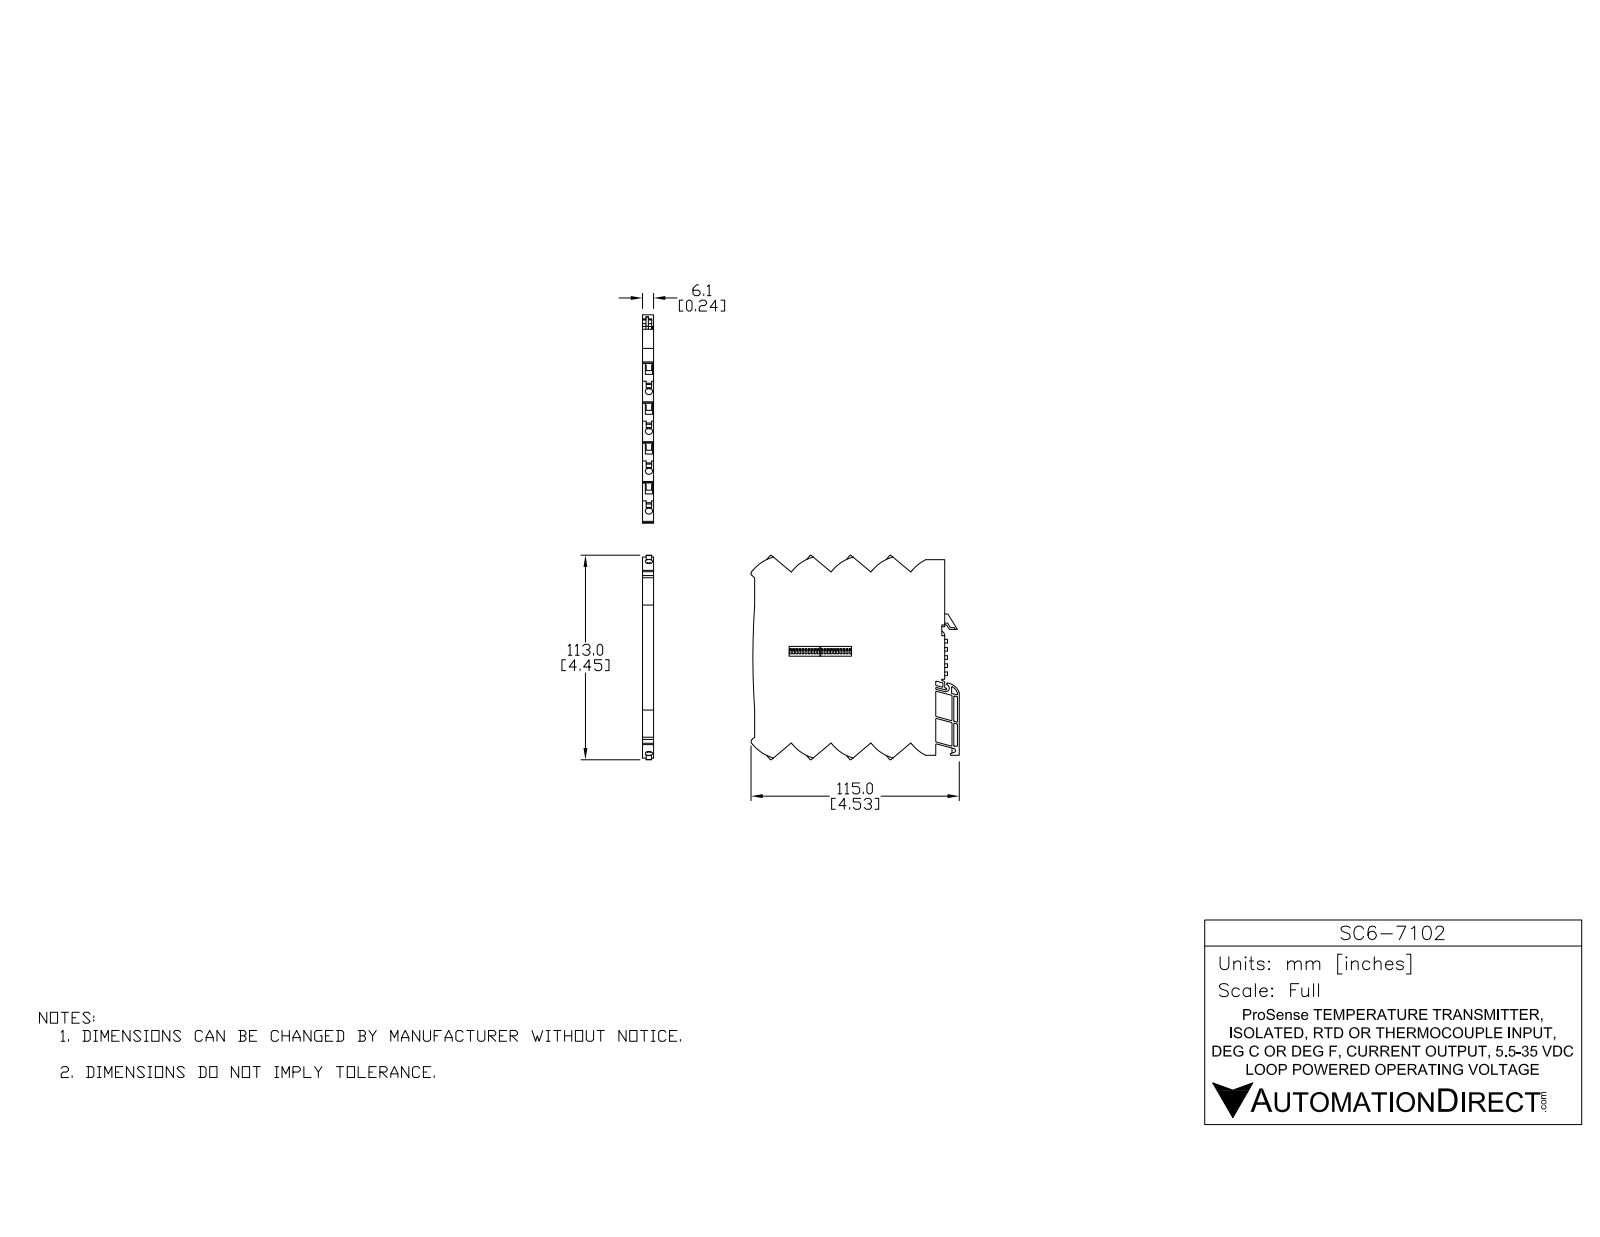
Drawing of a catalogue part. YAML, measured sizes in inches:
part_name: "SC6-7102"
step_written_by: "SolidWorks 2017 (AUTOMOTIVE_DESIGN)"
units: inches
bodies: {solids: 1, faces: 804, planar: 537, cylindrical: 107, other: 160}
overall_size: [4.528, 4.448, 0.24]
volume: 3.965
surface_area: 43.77
round_holes:
  - {diameter: 0.157, count: 8}
partial_cylinders:
  - {radius: 0.012, count: 33}
  - {radius: 0.02, count: 10}
  - {radius: 0.059, count: 10}
  - {radius: 0.918, count: 10}
  - {radius: 0.008, count: 2}
  - {radius: 0.022, count: 1}
  - {radius: 0.043, count: 1}
  - {radius: 0.079, count: 1}
face_to_face_distances: [0.24, 0.039, 0.118, 0.157, 0.081, 0.557, 0.041, 0.159, 0.138, 0.199]
hole_center_spacings: [0.557, 1.113, 0.557, 1.67]
